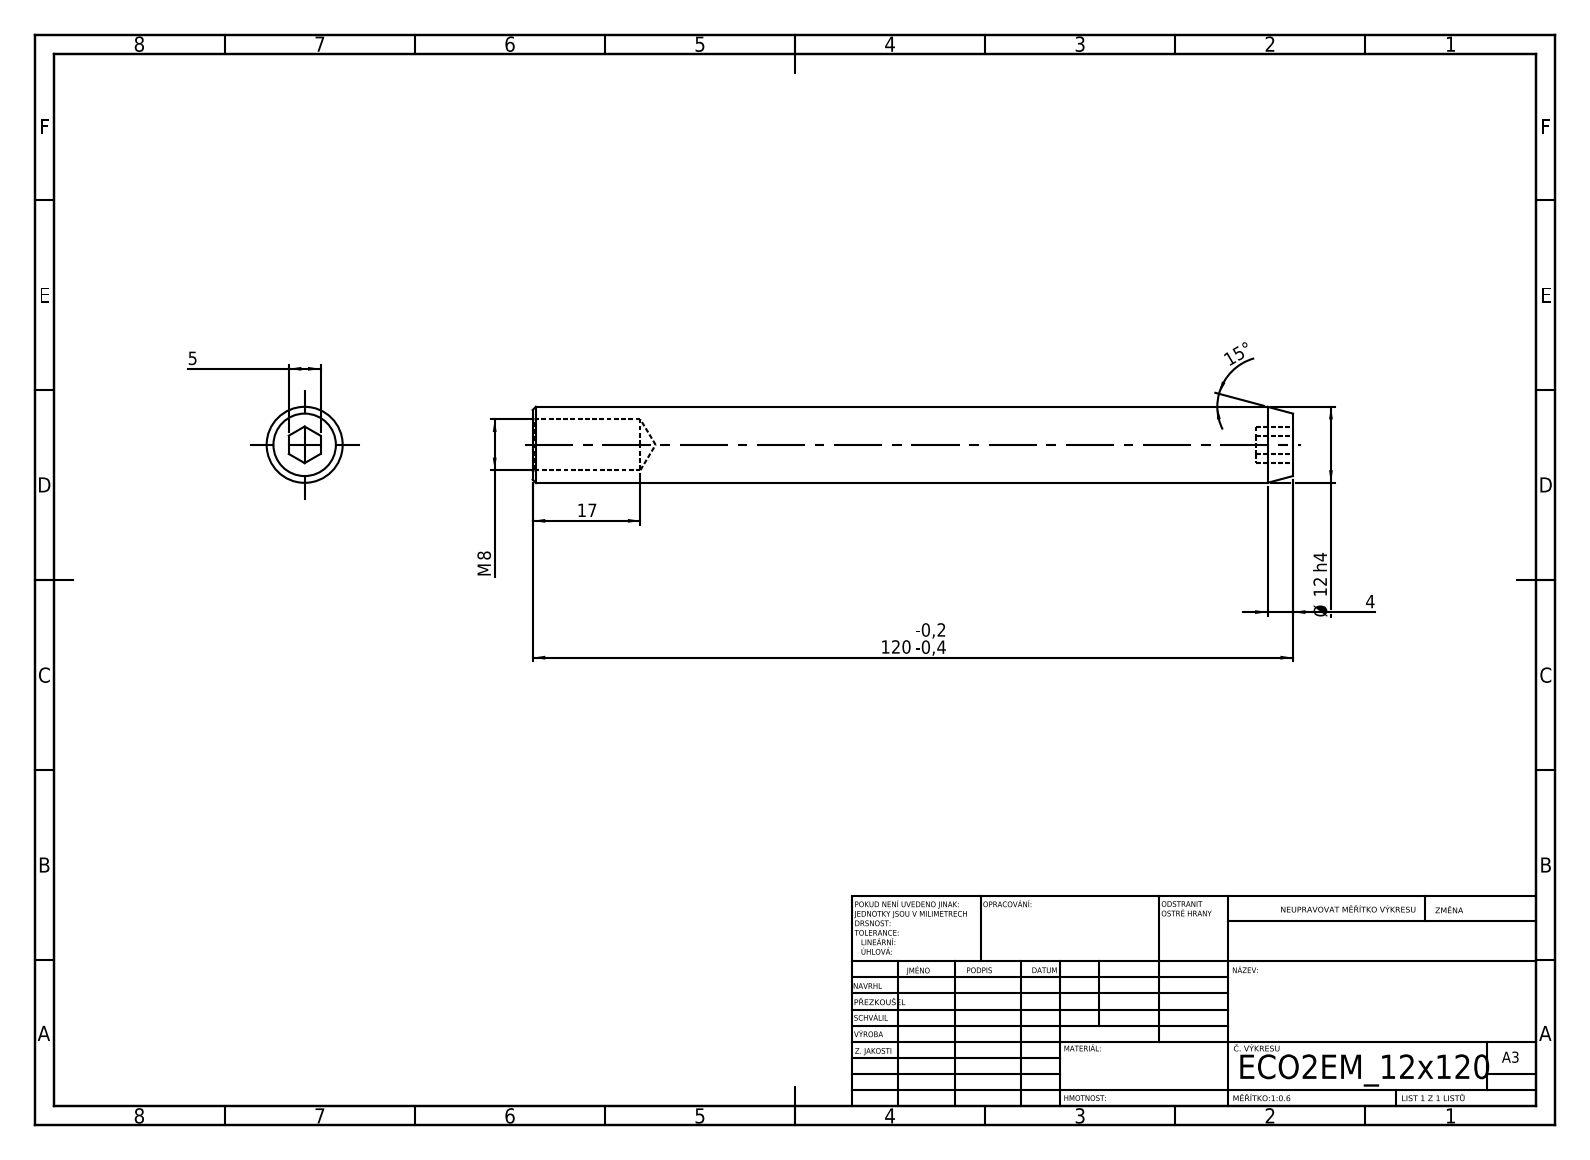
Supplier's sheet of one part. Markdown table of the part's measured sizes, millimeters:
| quantity | value |
| --- | --- |
| STEP written by | SolidWorks 2019 (CONFIG_CONTROL_DESIGN) |
| units | millimeters |
| bodies | 1 solid, 21 faces (9 planar, 4 cylindrical, 8 other) |
| overall size | 120 × 12 × 12 |
| volume | 12 470 mm³ |
| surface area | 5 226 mm² |
| round holes (diameter × count) | 8 × 1 |
| round bosses / shafts (diameter × count) | 12 × 1 |
| main face-to-face distances | 5, 120, 5.8, 114.2 |
